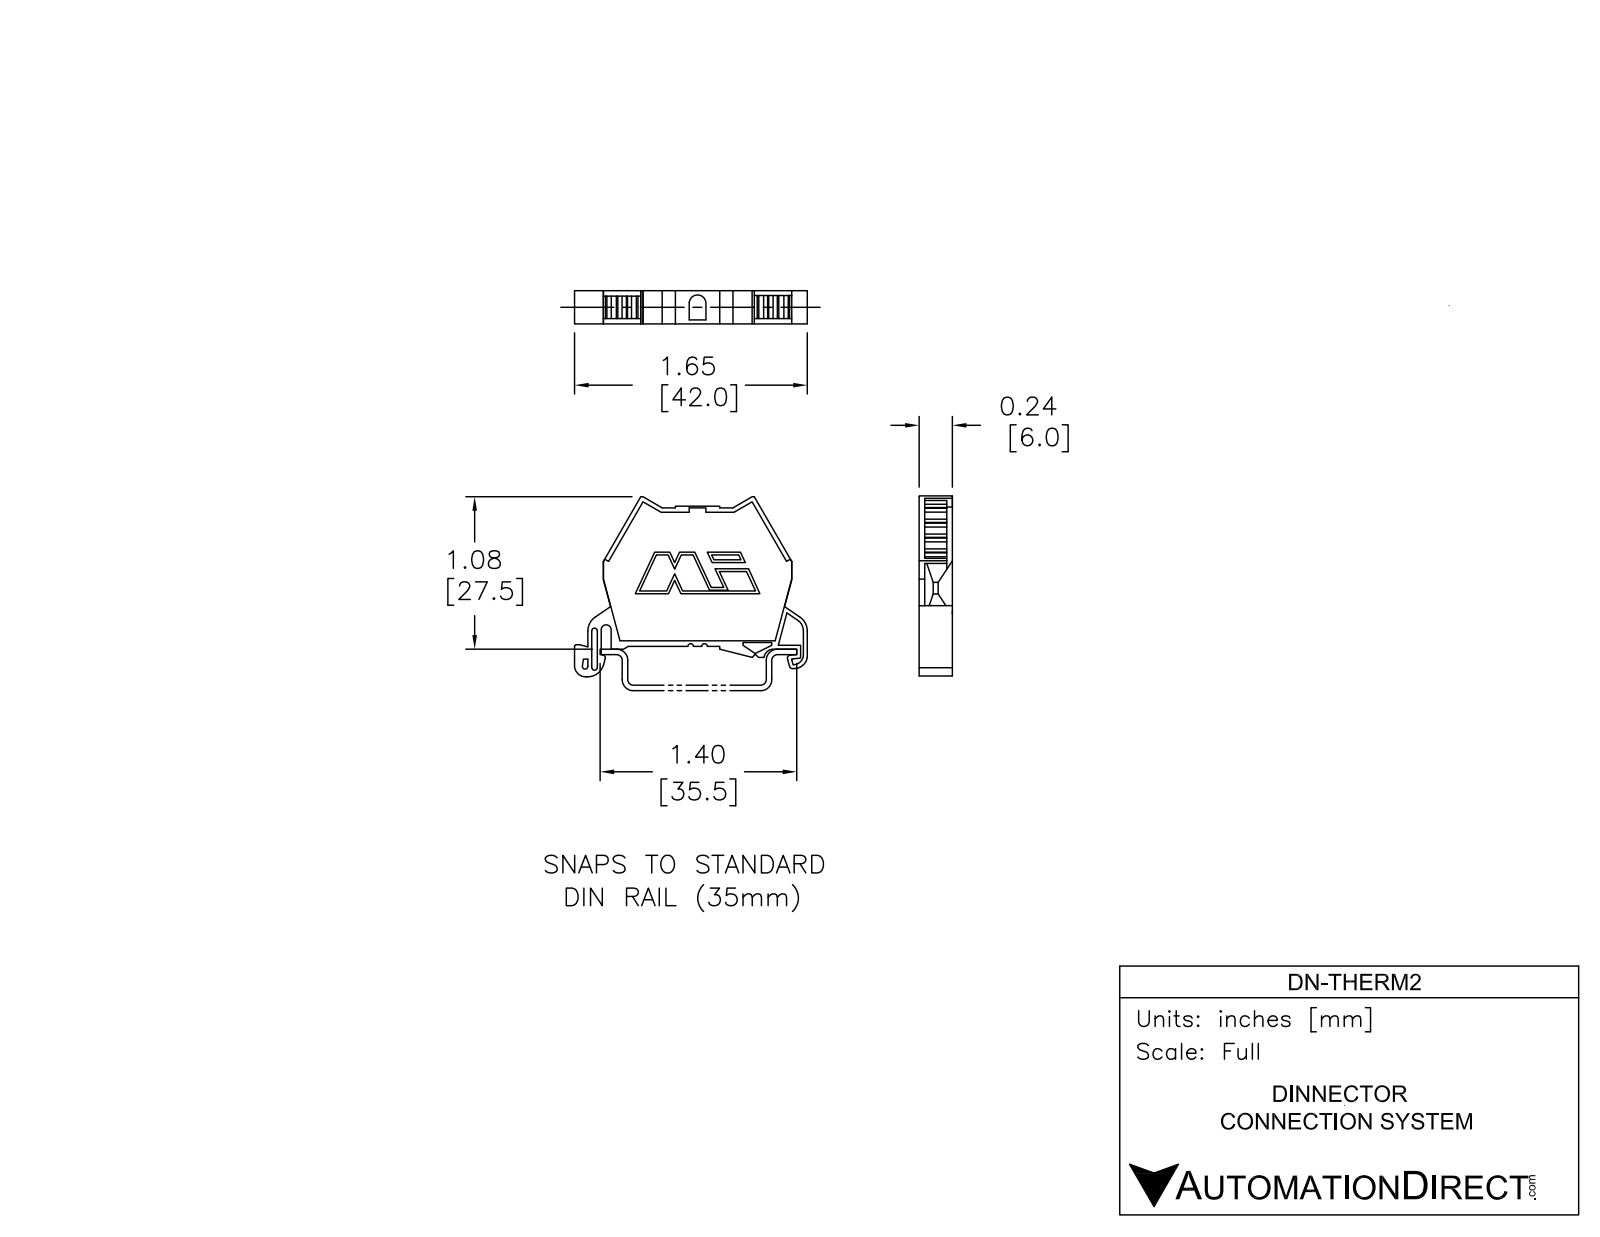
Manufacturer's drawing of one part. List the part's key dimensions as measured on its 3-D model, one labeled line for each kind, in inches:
Part name (STEP PRODUCT): 43610_DN-THERM2
STEP written by: SolidWorks 2013 (AUTOMOTIVE_DESIGN)
Units: inches
Bodies: 1 solid, 183 faces (162 planar, 21 cylindrical, 0 other)
Overall size (bounding box): 1.654 × 1.28 × 0.197
Volume: 0.248 in³ · Surface area: 4.543 in²
Partial cylindrical surfaces — rounded edges, fillets, slot ends (radius × count): R0.02 ×5, R0.118 ×3, R0.079 ×2, R0.012 ×1, R0.035 ×1, R0.063 ×1, R0.067 ×1, R0.087 ×1
Main face-to-face distances: 0.197, 0.024, 0.039, 0.118, 0.016, 0.157, 0.087, 0.173, 0.134, 0.094
